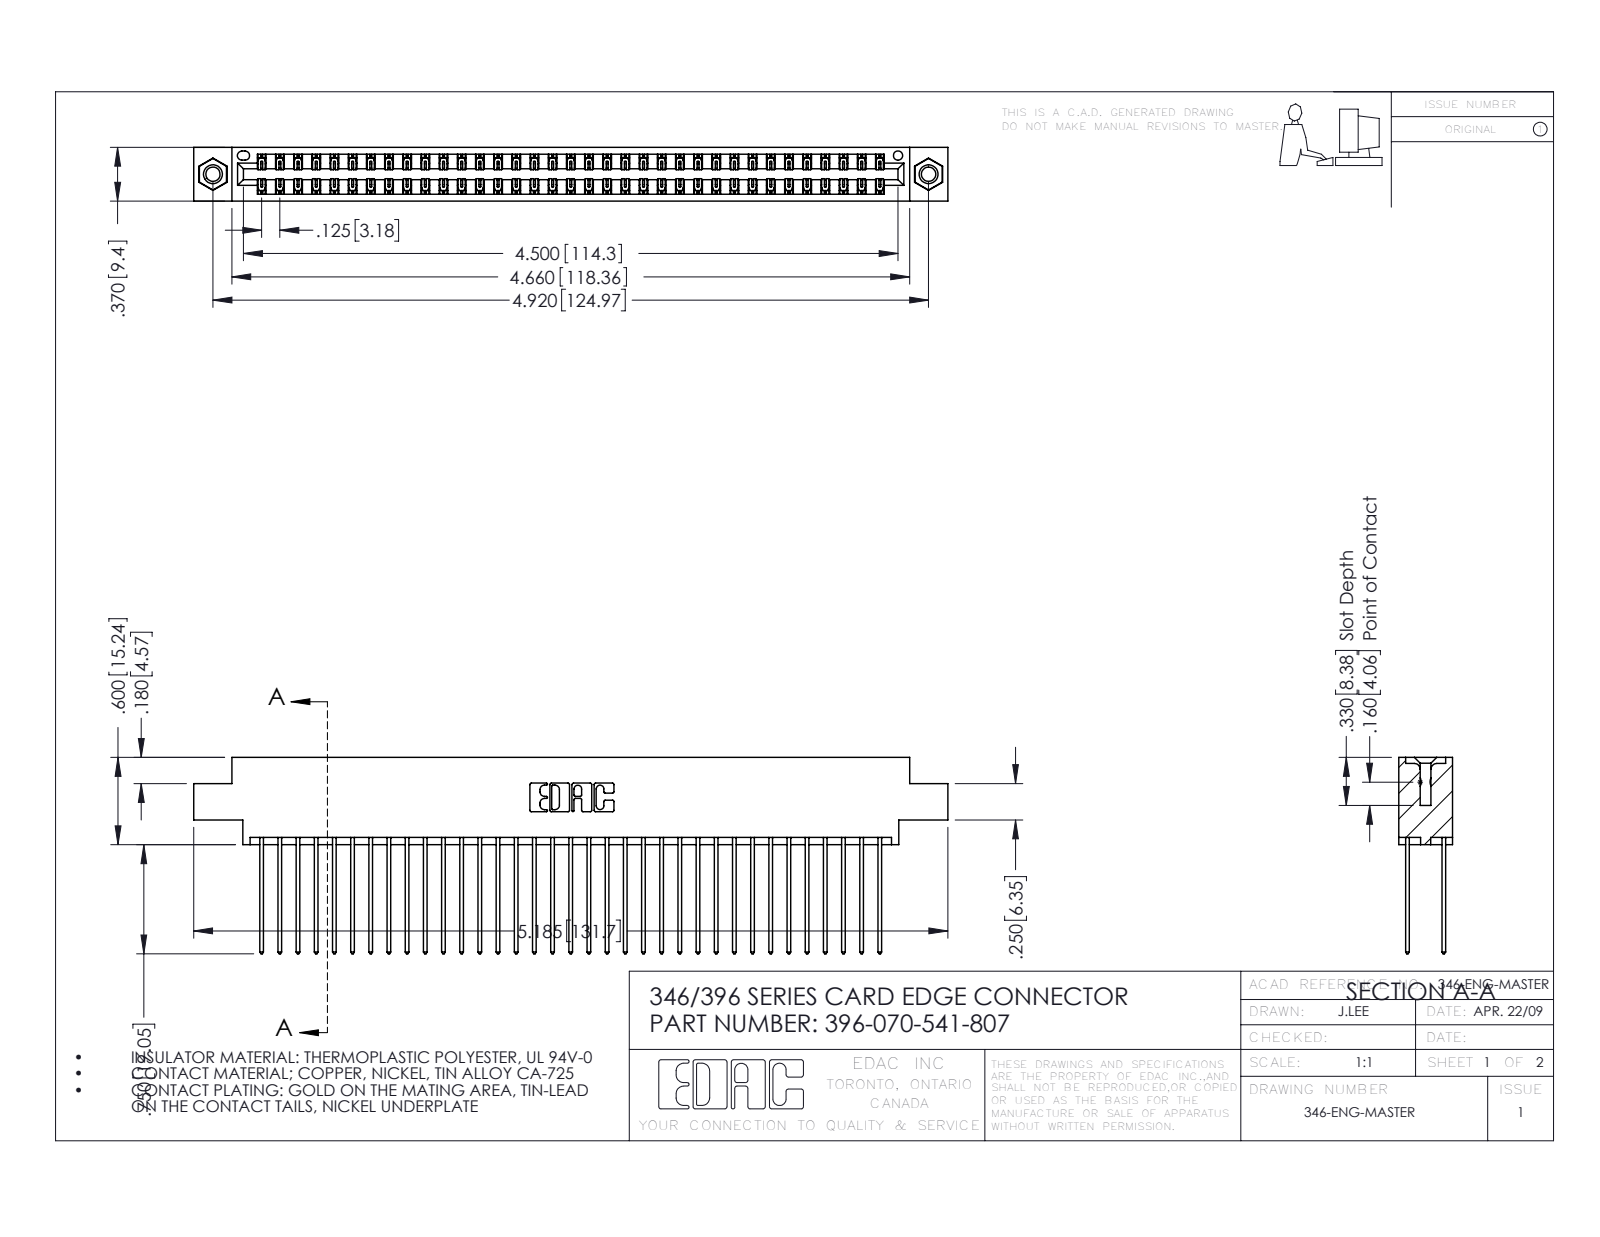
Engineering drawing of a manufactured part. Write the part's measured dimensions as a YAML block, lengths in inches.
part_name: "346 Part_0.170 Offset - 0.156 Dia-TI; 345-250-001_345-250-005-103; 345-292-001_345-293-141; 396-070-541-807"
step_written_by: "SolidWorks 2016 (CONFIG_CONTROL_DESIGN)"
units: inches
bodies: {solids: 73, faces: 3826, planar: 2562, cylindrical: 1248, other: 16}
overall_size: [5.185, 1.35, 0.37]
volume: 0.795
surface_area: 30.89
round_holes:
  - {diameter: 0.098, count: 2}
  - {diameter: 0.125, count: 2}
  - {diameter: 0.156, count: 2}
  - {diameter: 0.064, count: 1}
round_bosses_or_shafts:
  - {diameter: 0.155, count: 2}
partial_cylinders:
  - {radius: 0.006, count: 105}
  - {radius: 0.01, count: 70}
  - {radius: 0.01, count: 22}
  - {radius: 0.007, count: 6}
  - {radius: 0.031, count: 6}
  - {radius: 0.026, count: 3}
  - {radius: 0.014, count: 2}
  - {radius: 0.022, count: 2}
face_to_face_distances: [0.048, 0.322, 0.25, 0.072, 0.298, 0.025, 0.37, 0.275, 0.222, 0.225]
hole_center_spacings: [0.246, 4.711, 4.92]
